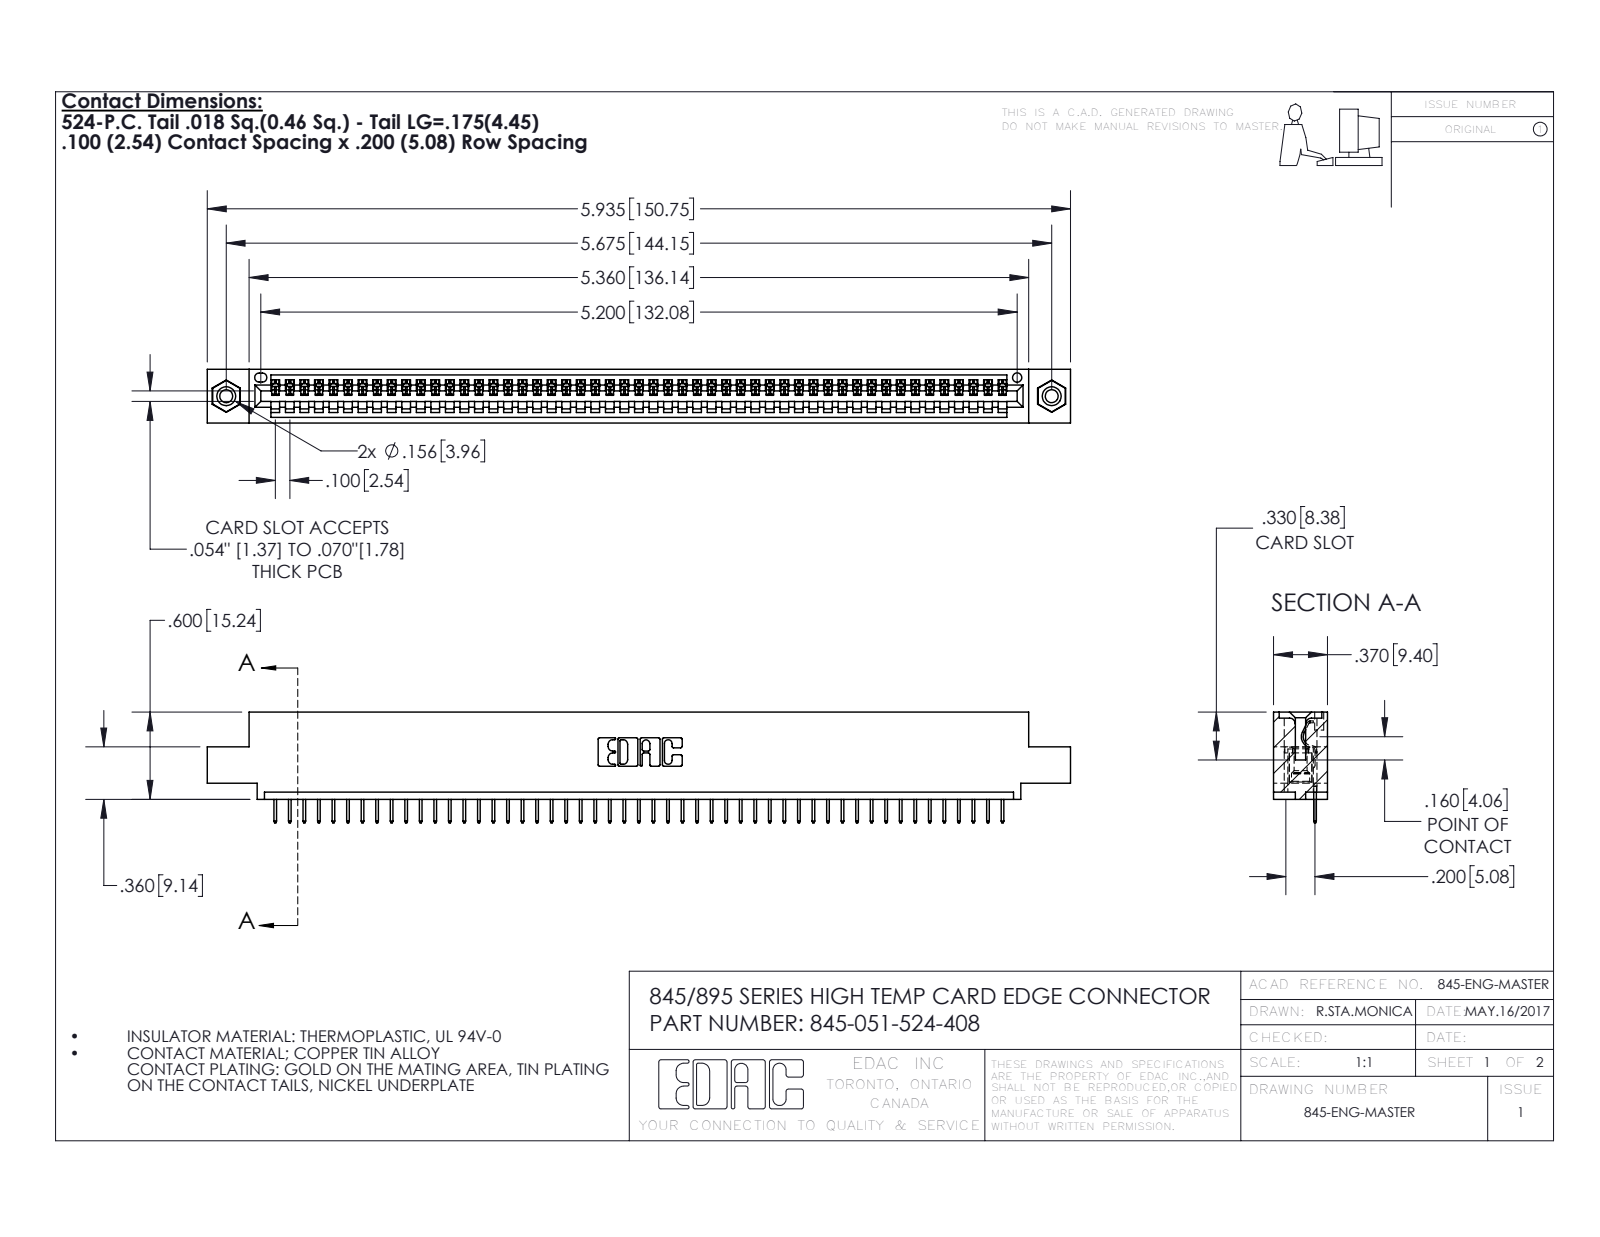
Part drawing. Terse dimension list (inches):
name: 345-292-001_345-293-124; 345 Part_0.110 Offset - 0.156 Dia-TI; 345-051-524-408; 345-250-001_345-250-003-102
written by: SolidWorks 2016 (CONFIG_CONTROL_DESIGN)
unit: in
bodies: 54 solids, 3352 faces (2462 planar, 874 cylindrical, 16 other)
size: 5.935 × 0.762 × 0.37
volume: 0.861 in³; area: 28.41 in²
holes: 2× ⌀0.089, 2× ⌀0.125, 2× ⌀0.156, 1× ⌀0.064
bosses: 2× ⌀0.155
rounds: 102× R0.006, 22× R0.01, 6× R0.007, 6× R0.031, 3× R0.026, 2× R0.031, 2× R0.04, 1× R0.014
face distances: 0.072, 0.298, 0.37, 0.2, 0.098, 0.272, 0.025, 0.225, 0.072, 0.149
hole spacings: 0.27, 5.439, 5.675
